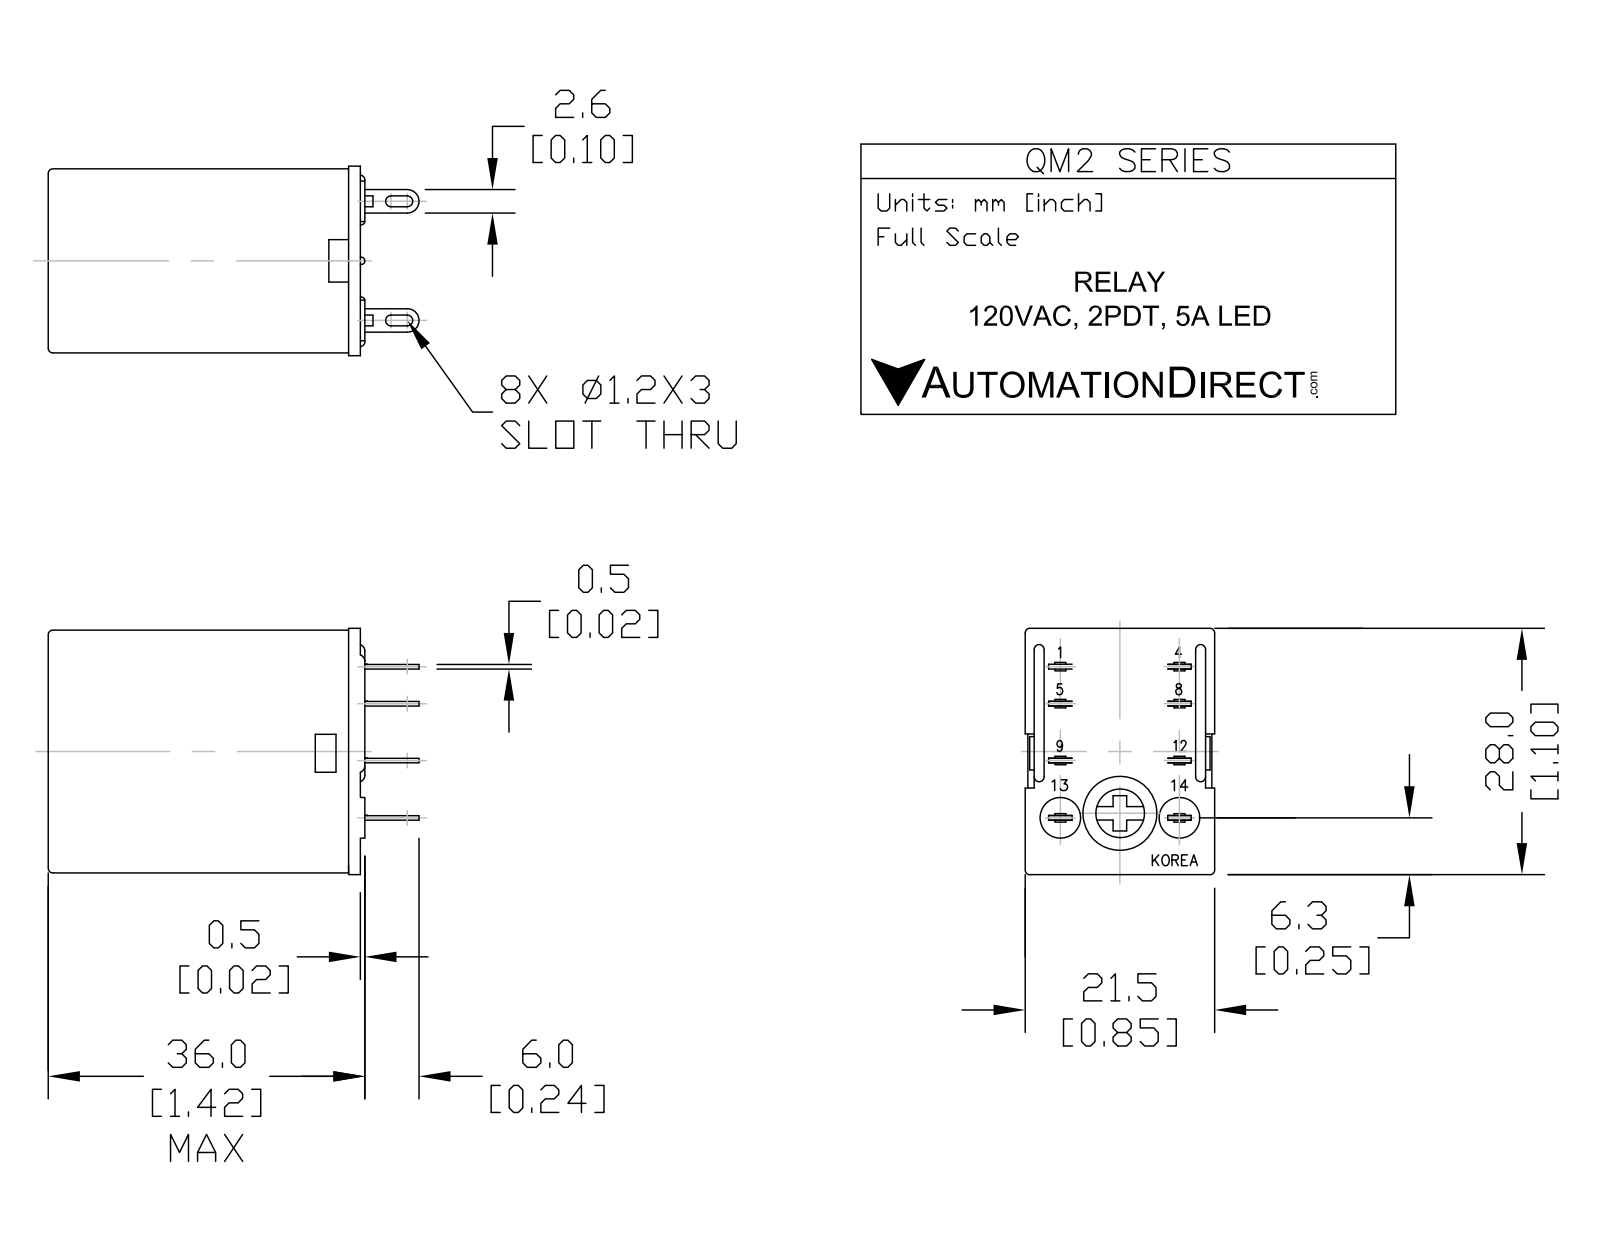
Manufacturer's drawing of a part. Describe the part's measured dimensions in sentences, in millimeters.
The part is named "QM2N1-A220". Its 3-D file was written by "SolidWorks 2013 (AUTOMOTIVE_DESIGN)". It is 1 solid with 183 faces: 119 planar, 60 cylindrical and 4 other. Overall it measures 42 by 28 by 21.5 millimeters. Its volume is 19 242 cubic millimeters and its surface area 4 802 square millimeters. Round holes: 1 of diameter 6.5. Round bosses or shafts: 2 of diameter 4.2, 1 of diameter 4. Partial cylindrical surfaces (rounded edges, fillets, slot ends): 12 of radius 1, 4 of radius 0.5, 4 of radius 0.6. The main face-to-face distances are 35.5, 0.5, 6.5, 36, 6, 11, 4.5, 2, 7, 13.
